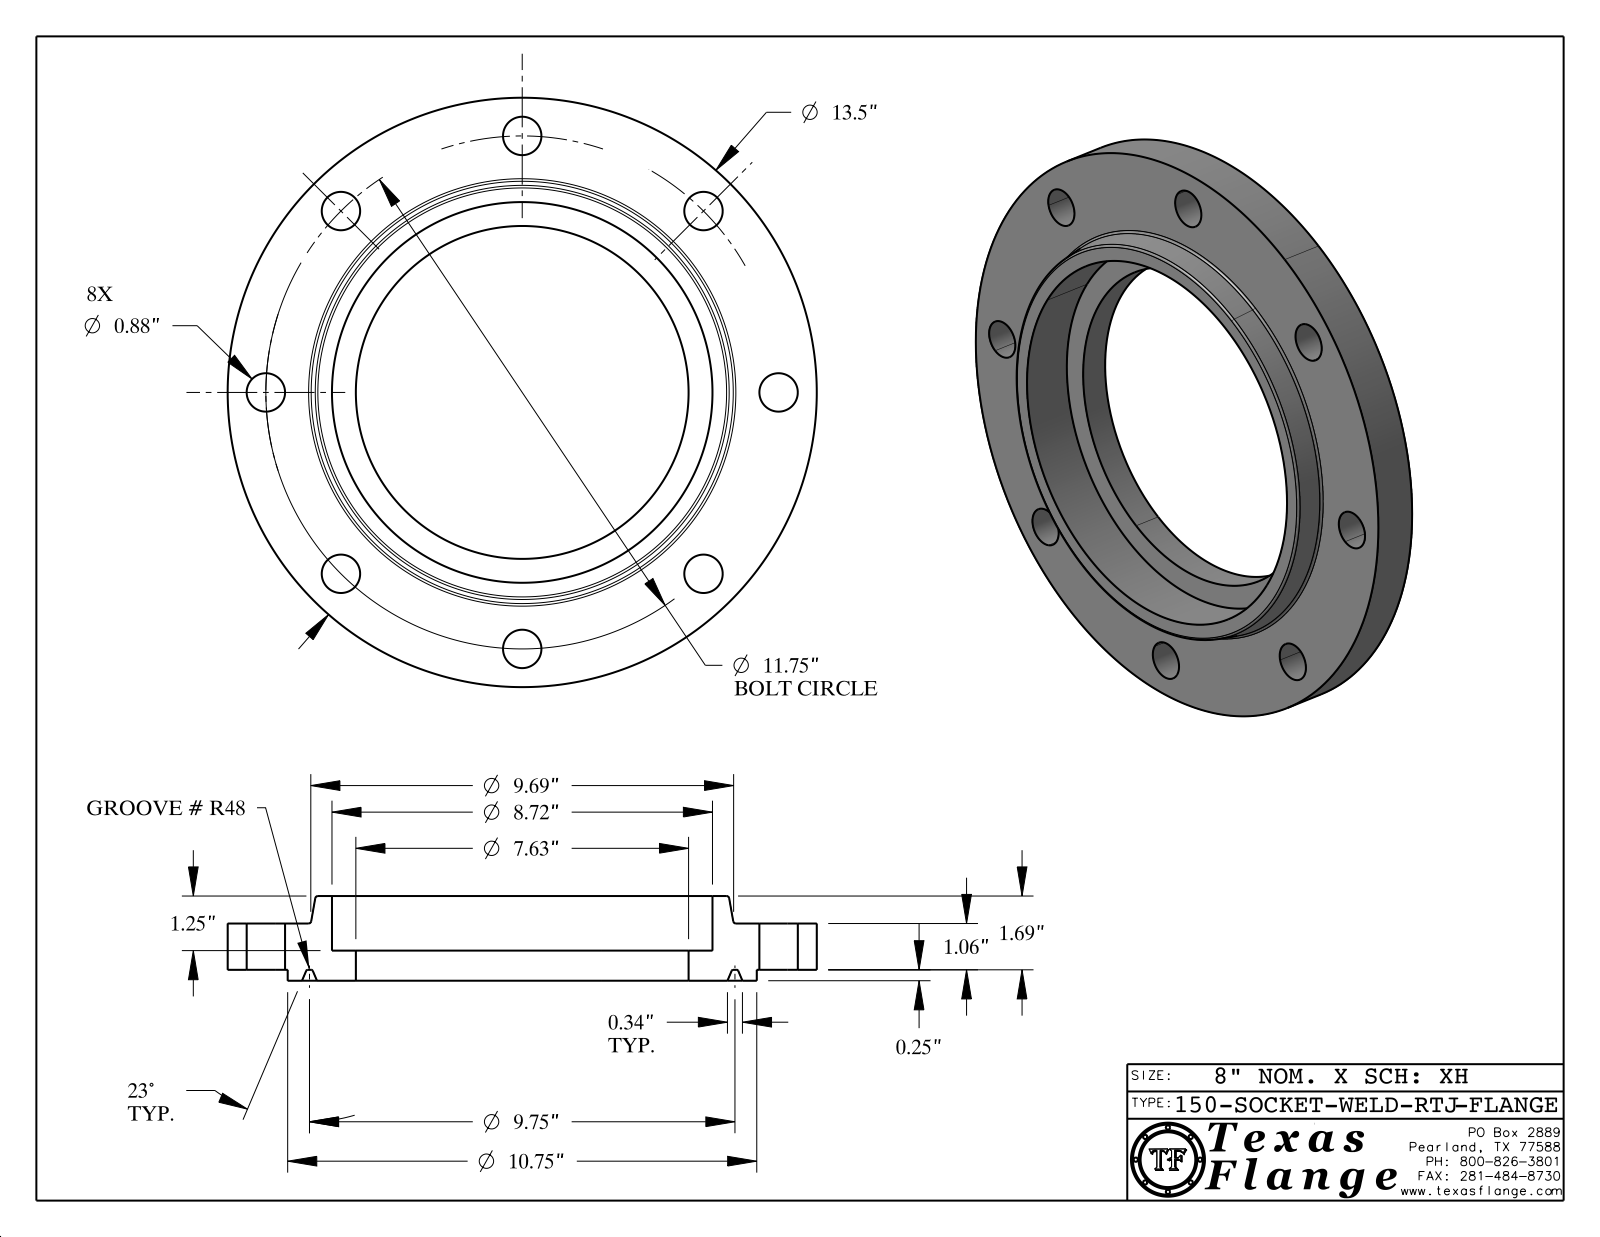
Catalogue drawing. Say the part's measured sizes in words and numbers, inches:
The part is named "150-SOCKET-WELD-RTJ". Its 3-D file was written by "CATIA V5 STEP AP214 (AUTOMOTIVE_DESIGN)". It is 1 solid with 430 faces: 372 planar, 44 cylindrical and 14 other. Overall it measures 13.5 by 13.5 by 1.94 inches. Its volume is 106.7 cubic inches and its surface area 337.7 square inches. Round holes: 8 of diameter 0.88, 1 of diameter 0.495, 1 of diameter 7.625, 1 of diameter 8.72. Round bosses or shafts: 8 of diameter 0.03, 1 of diameter 13.5, 1 of diameter 10.75, 1 of diameter 0.39. The main face-to-face distances are 1.06, 0.25, 1.31, 0.69, 0.44, 0.62, 1.94, 1.69, 1.25, 0.63. The hole center spacings are 5.875, 4.496, 8.309, 10.856, 11.75, 9.77, 2.292, 2.293.
